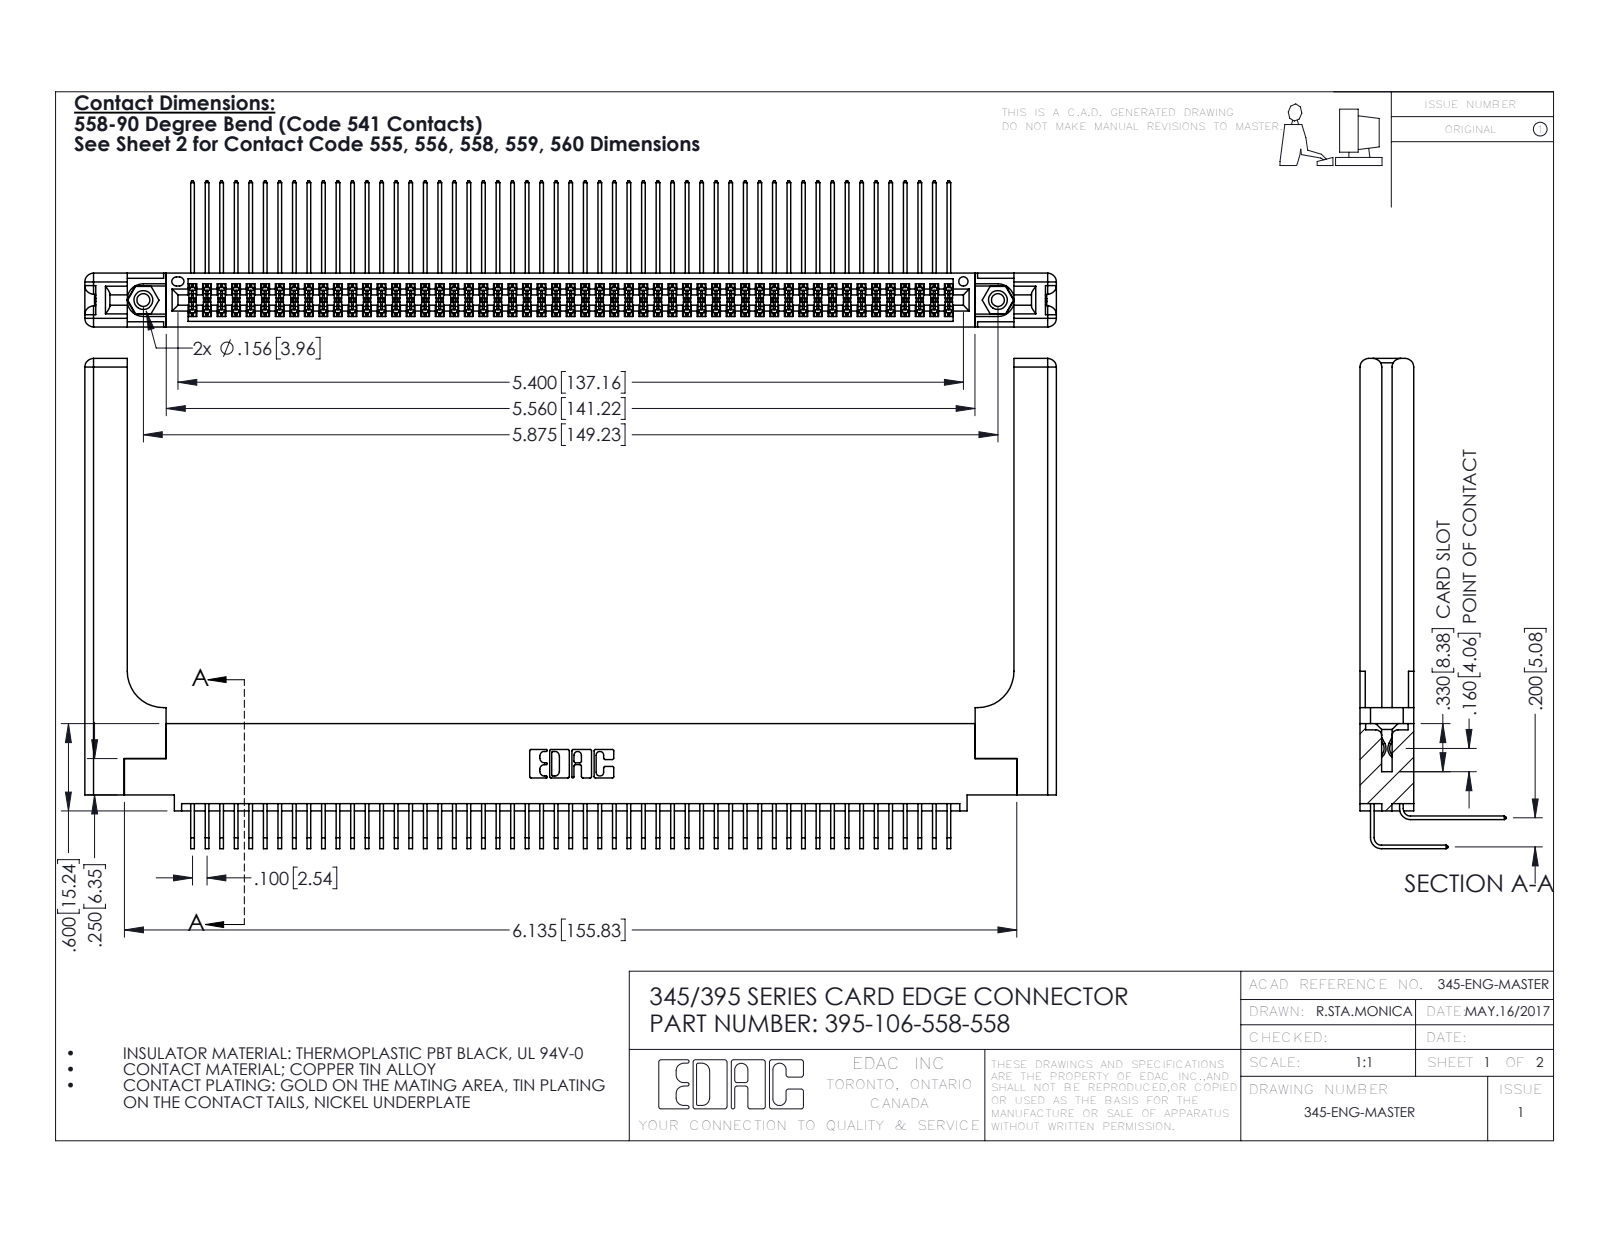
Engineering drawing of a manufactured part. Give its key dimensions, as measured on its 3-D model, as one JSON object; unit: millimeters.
{"part_name": "345-292-001_558 559 Tail - 1; 345-292-001_558 Tail - 2; 345-220-058_345-220-058; 345 Part_0.110 Offset - 0.156 Dia-TH (+2 more)", "step_written_by": "SolidWorks 2016 (CONFIG_CONTROL_DESIGN)", "units": "millimeters", "bodies": {"solids": 111, "faces": 5898, "planar": 3942, "cylindrical": 1896, "other": 60}, "overall_size": [169.6, 85.6, 25.5], "volume_mm3": 25600, "surface_area_mm2": 33550, "round_holes": [[2.3, 2], [3.2, 2], [4, 2], [1.6, 1]], "round_bosses_or_shafts": [[3.9, 2]], "partial_cylinders_radius": [[0.2, 160], [0.3, 22], [1.5, 16], [0.2, 6], [0.8, 6], [0.7, 3], [0.4, 2], [0.5, 2]], "face_to_face_distances": [1.8, 7.6, 9.4, 5.1, 2.5, 6.9, 0.6, 5.7, 3.8, 3.8], "hole_center_spacings": [6.9, 143.2, 149.2]}
